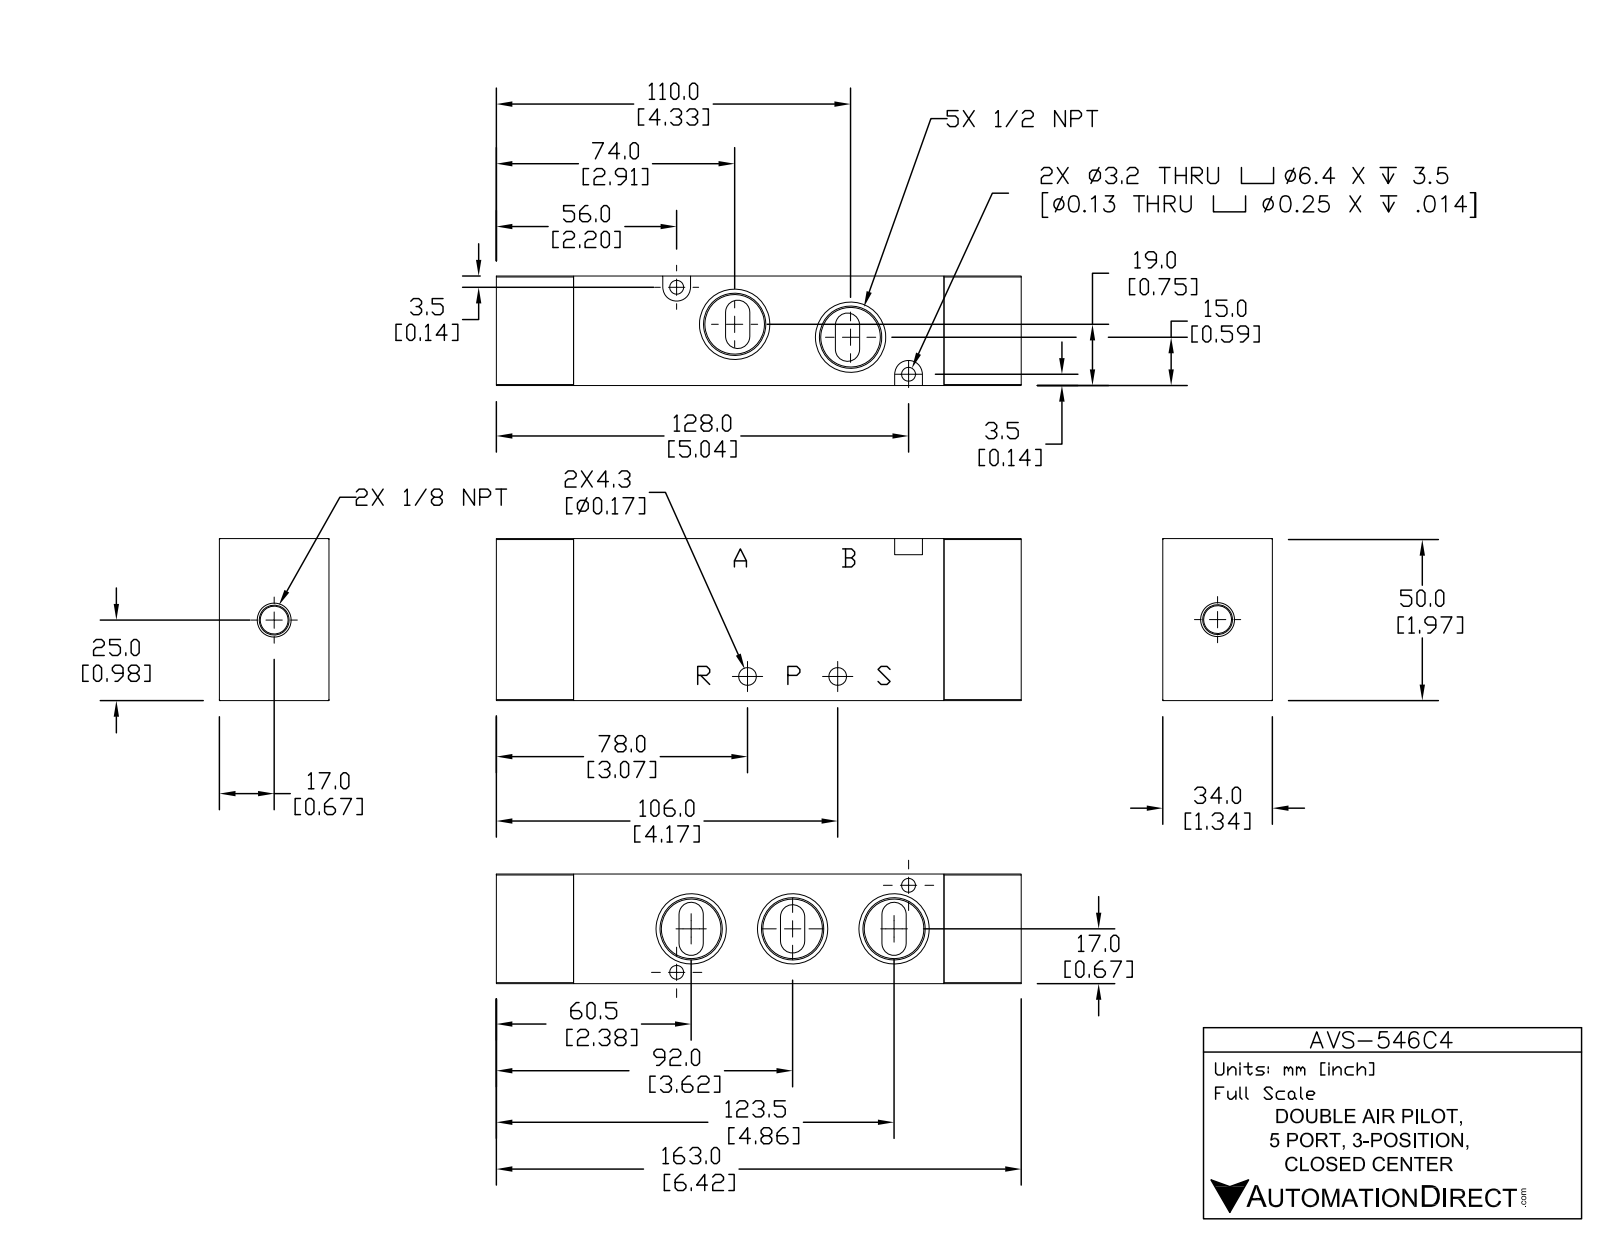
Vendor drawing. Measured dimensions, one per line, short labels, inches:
name: AVS-546C4
written by: SolidWorks 2015 (CONFIG_CONTROL_DESIGN)
unit: in
bodies: 3 solids, 108 faces (46 planar, 34 cylindrical, 28 other)
size: 6.417 × 1.969 × 1.339
volume: 15.16 in³; area: 70.65 in²
holes: 2× ⌀0.169, 2× ⌀0.217
rounds: 10× R0.148, 4× R0.012, 2× R0.169
face distances: 1.339, 1.969, 4.528, 0.945, 5.472, 6.417, 0.579, 1.389, 0.787, 1.181
hole spacings: 1.102, 3.028
